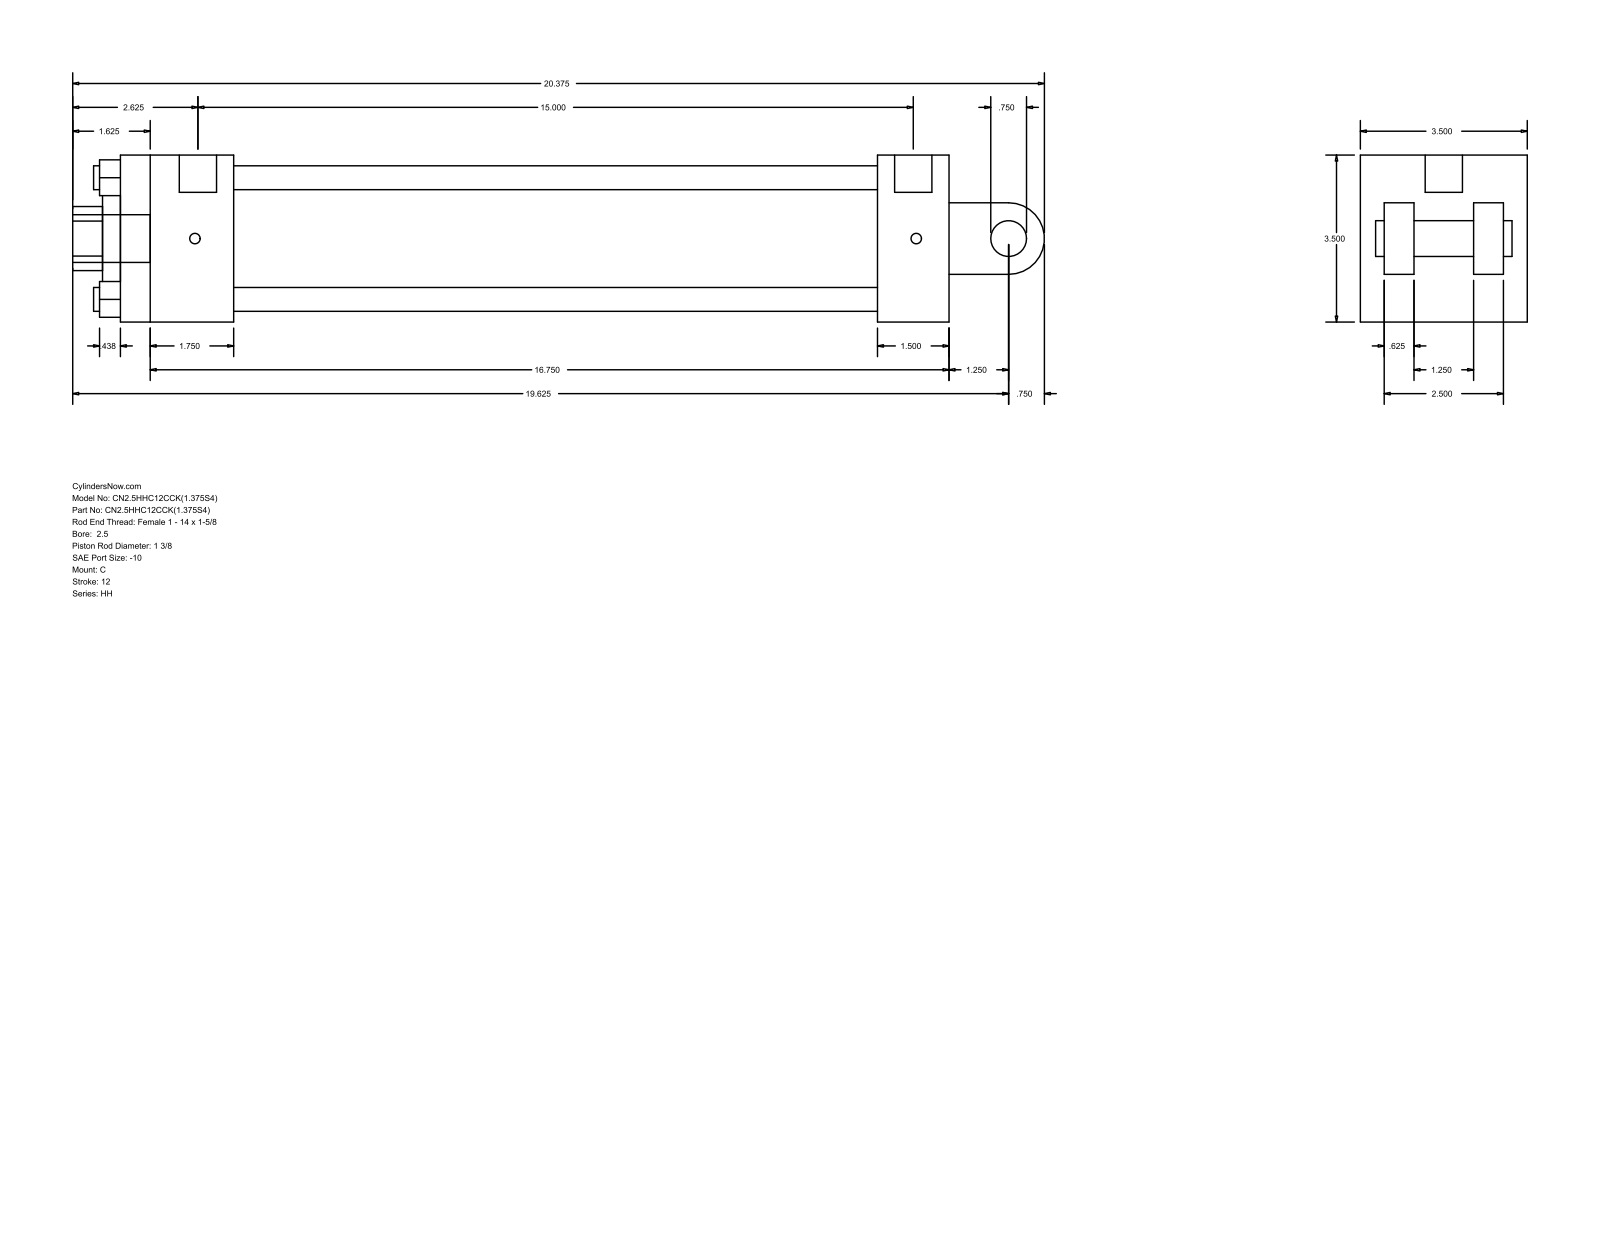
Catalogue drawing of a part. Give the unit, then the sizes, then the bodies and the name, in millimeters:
Units: millimetres
Overall size (bounding box): 517.52 × 88.9 × 88.9
Round holes (diameter × count): ⌀12.7 ×4, ⌀5.56 ×2, ⌀19.84 ×1, ⌀34.92 ×1, ⌀50.8 ×1, ⌀73.03 ×1
Round bosses / shafts (diameter × count): ⌀5.56 ×2, ⌀25.4 ×1, ⌀19.84 ×1, ⌀19.05 ×1
Partial cylindrical surfaces — rounded edges, fillets, slot ends (radius × count): R17.06 ×1, R19.05 ×1
Main face-to-face distances: 88.9, 441.33, 63.5, 15.87, 12.7, 403.22, 38.11, 60.32, 342.9, 381.01
Hole centre spacings: 45.79, 64.76, 91.58, 1.58
Bodies: 0 solids, 99 faces (70 planar, 29 cylindrical, 0 other)
Part name (STEP PRODUCT): HH_C__0250_1.375
STEP written by: GSSL Pune (CONFIG_CONTROL_DESIGN)
